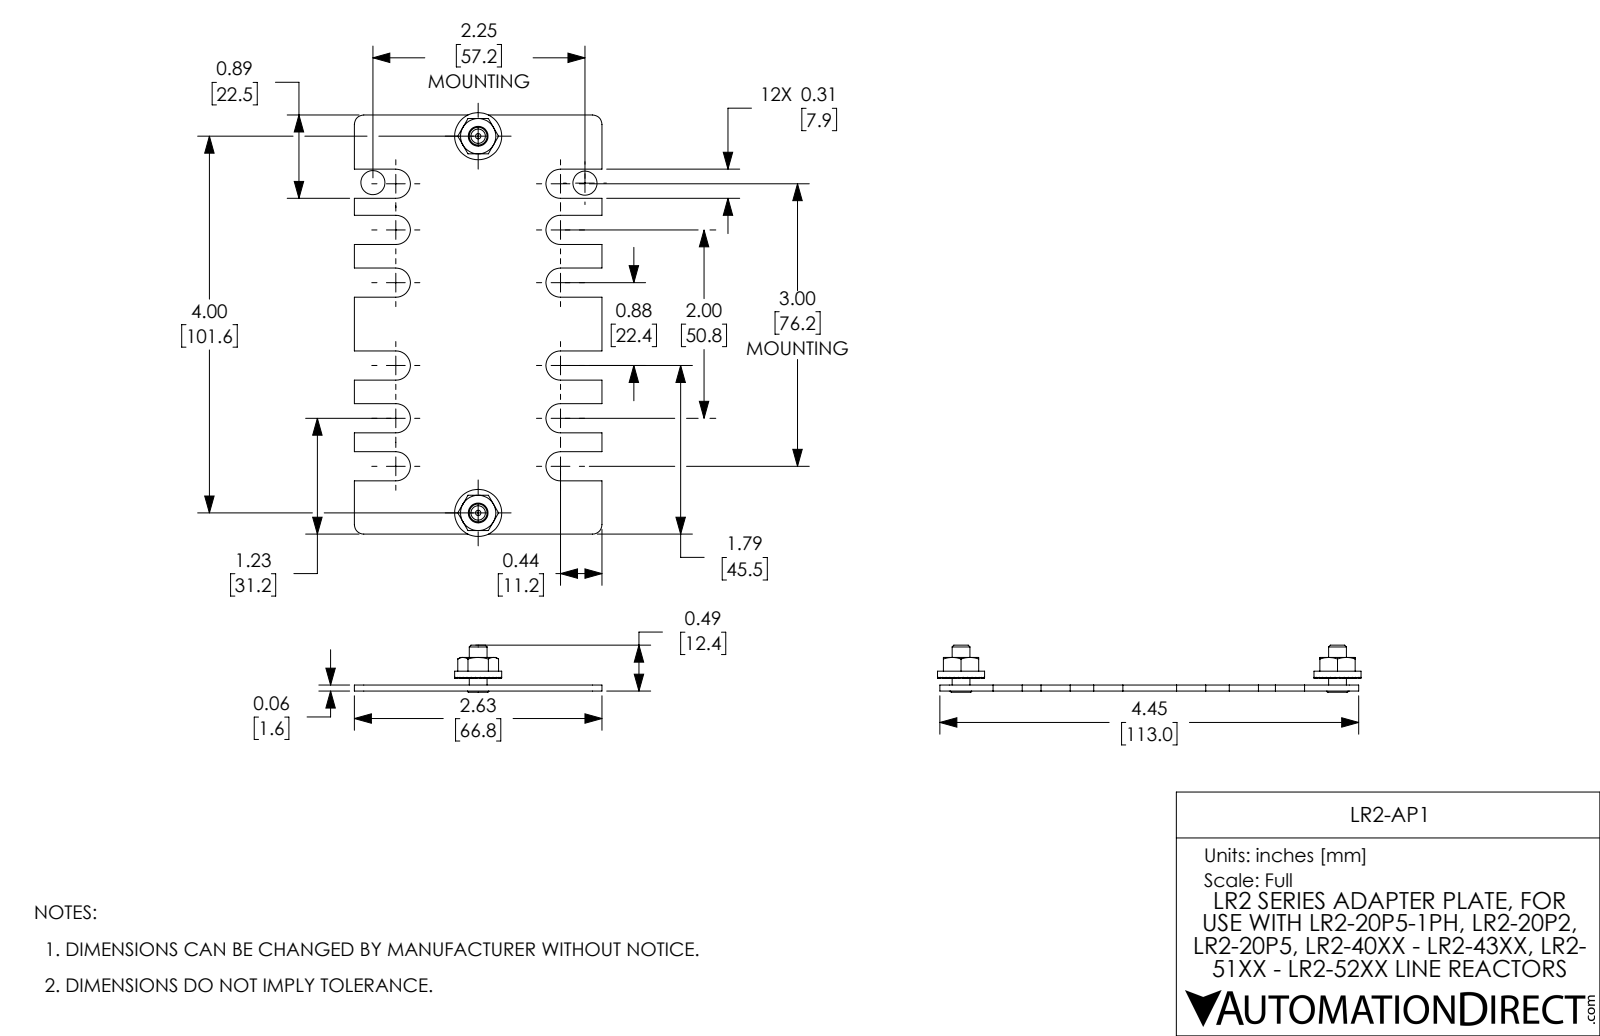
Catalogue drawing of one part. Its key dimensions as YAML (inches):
part_name: "LR2-AP1 r1"
step_written_by: "SolidWorks 2017 (AUTOMOTIVE_DESIGN)"
units: inches
bodies: {solids: 5, faces: 351, planar: 194, cylindrical: 90, other: 67}
overall_size: [4.5, 2.63, 0.5]
volume: 0.688
surface_area: 23.28
round_holes:
  - {diameter: 0.149, count: 2}
  - {diameter: 0.189, count: 2}
  - {diameter: 0.19, count: 2}
round_bosses_or_shafts:
  - {diameter: 0.5, count: 2}
  - {diameter: 0.37, count: 2}
  - {diameter: 0.19, count: 1}
partial_cylinders:
  - {radius: 0.155, count: 12}
  - {radius: 0.1, count: 4}
face_to_face_distances: [0.063, 2, 0.31, 4.45, 2.63, 0.293, 0.357, 0.146, 0.148, 0.211]
hole_center_spacings: [4]
